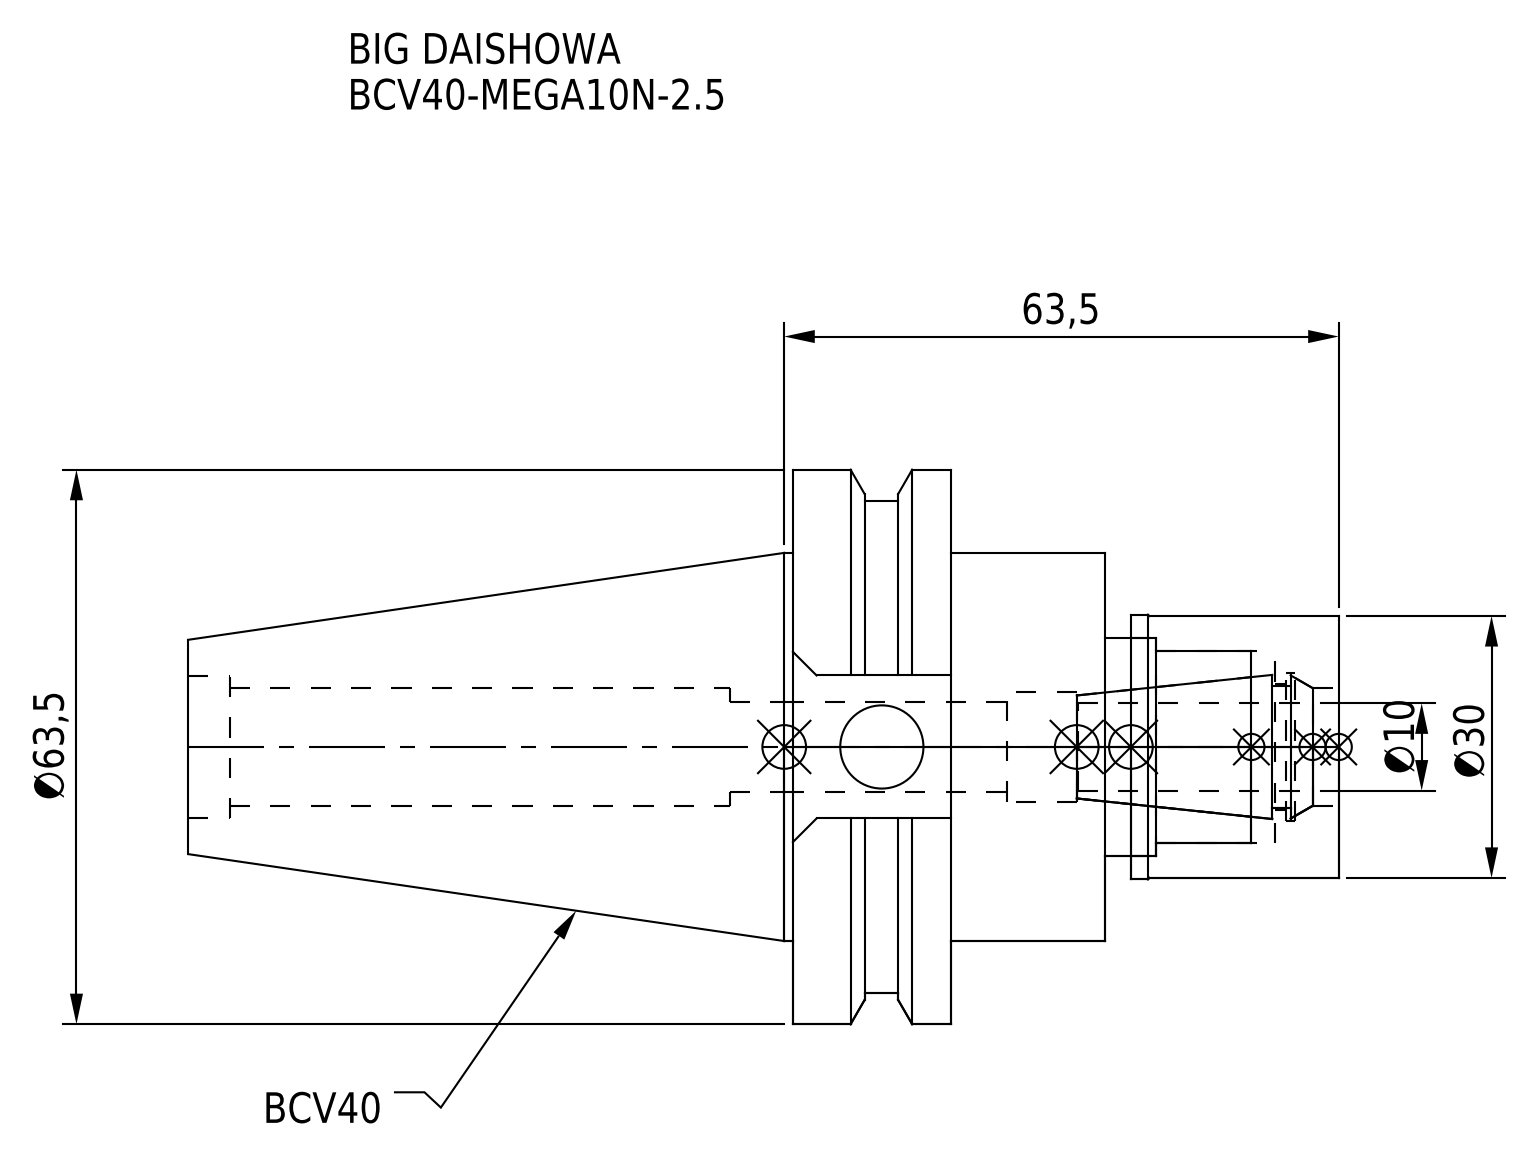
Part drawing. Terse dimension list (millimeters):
name: MGN10_1.stp; BCV40-MEGA10N-2_5-100.stp; BCV40MN10025-100_ASM.stp; BCV40-MEGA10N-2_5-100-FreeParts (+3 more)
written by: SolidWorks 2019 (CONFIG_CONTROL_DESIGN)
unit: mm
bodies: 2 solids, 83 faces (31 planar, 40 cylindrical, 12 other)
size: 131.75 × 63.5 × 61.35
volume: 144 232 mm³; area: 30 318 mm²
holes: 1× ⌀9.53, 1× ⌀10.4, 1× ⌀12.5, 1× ⌀13.5, 1× ⌀13.6, 1× ⌀14.5, 1× ⌀16.32, 1× ⌀17, 1× ⌀22, 1× ⌀25
bosses: 1× ⌀63.5, 1× ⌀56.36, 1× ⌀44.45, 1× ⌀30.3, 1× ⌀30
face distances: 18.05, 17.65, 35.7, 44.45, 26.8, 62.5, 131.75, 104.95, 87.3, 69.25
